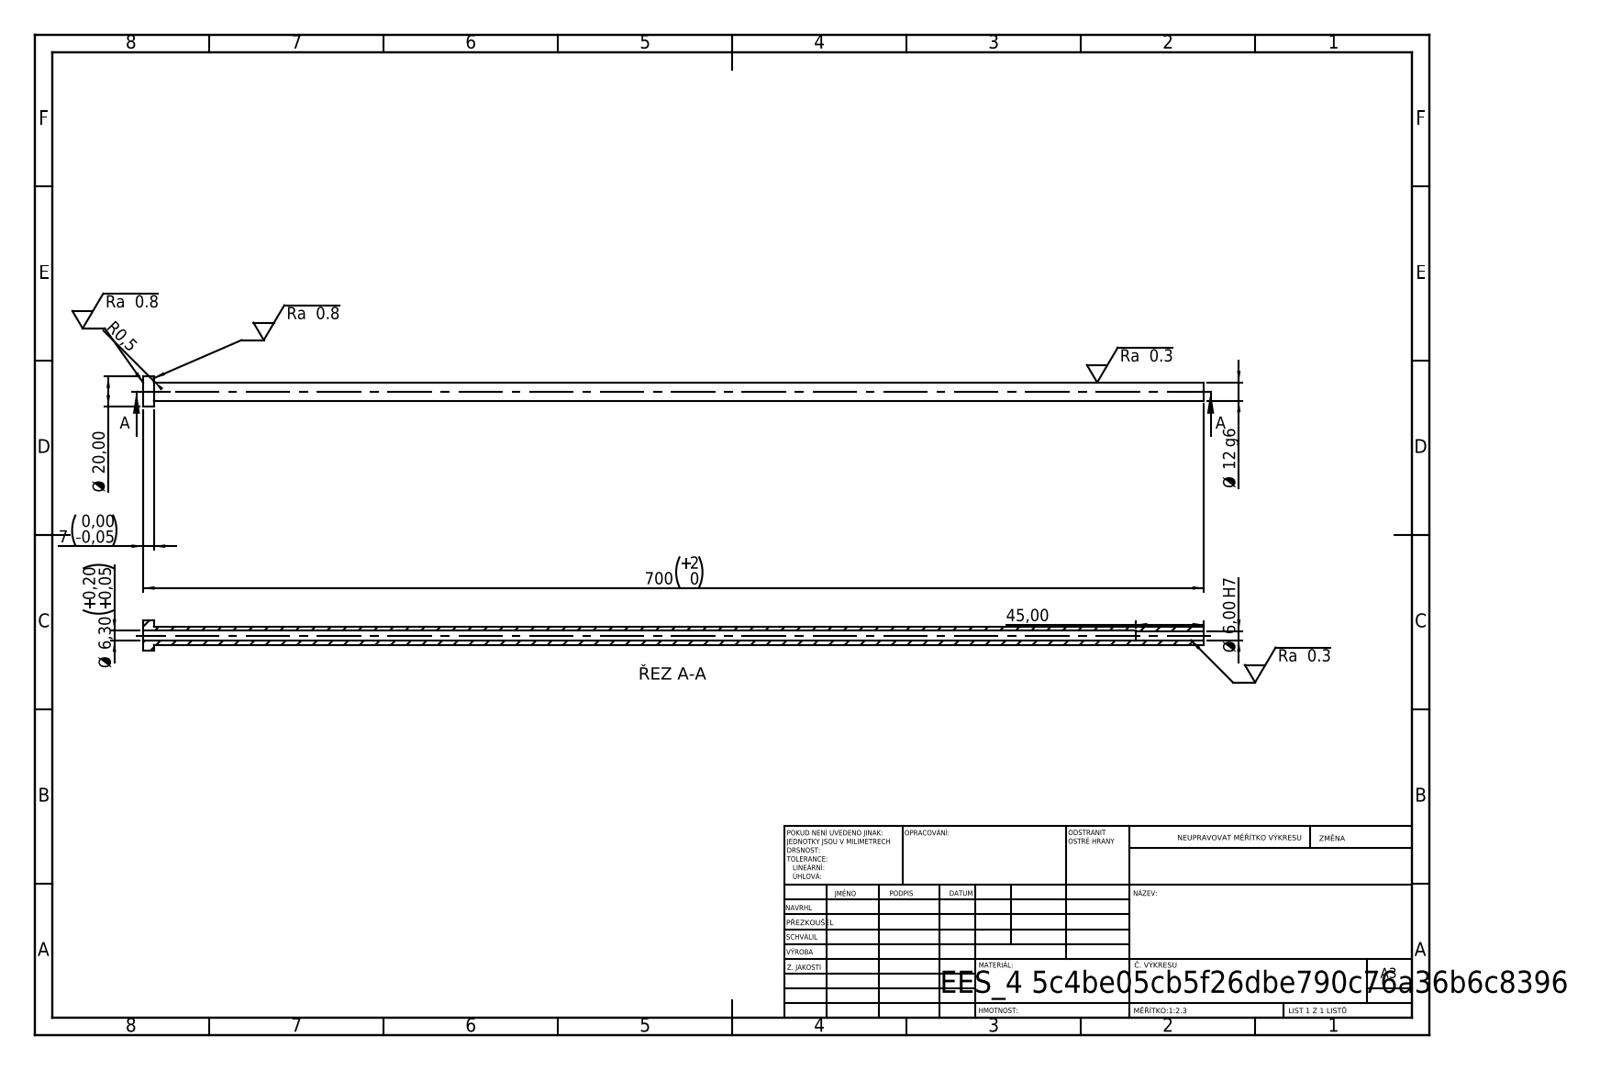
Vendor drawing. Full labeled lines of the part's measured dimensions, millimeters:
STEP written by: SolidWorks 2019 (CONFIG_CONTROL_DESIGN)
Units: millimetres
Bodies: 1 solid, 14 faces (4 planar, 8 cylindrical, 2 other)
Overall size (bounding box): 700 × 20 × 20
Volume: 58 887 mm³ · Surface area: 40 941 mm²
Round holes (diameter × count): ⌀6 ×1, ⌀6.3 ×1
Round bosses / shafts (diameter × count): ⌀20 ×1, ⌀12 ×1
Main face-to-face distances: 7, 700, 693, 655, 648, 45
